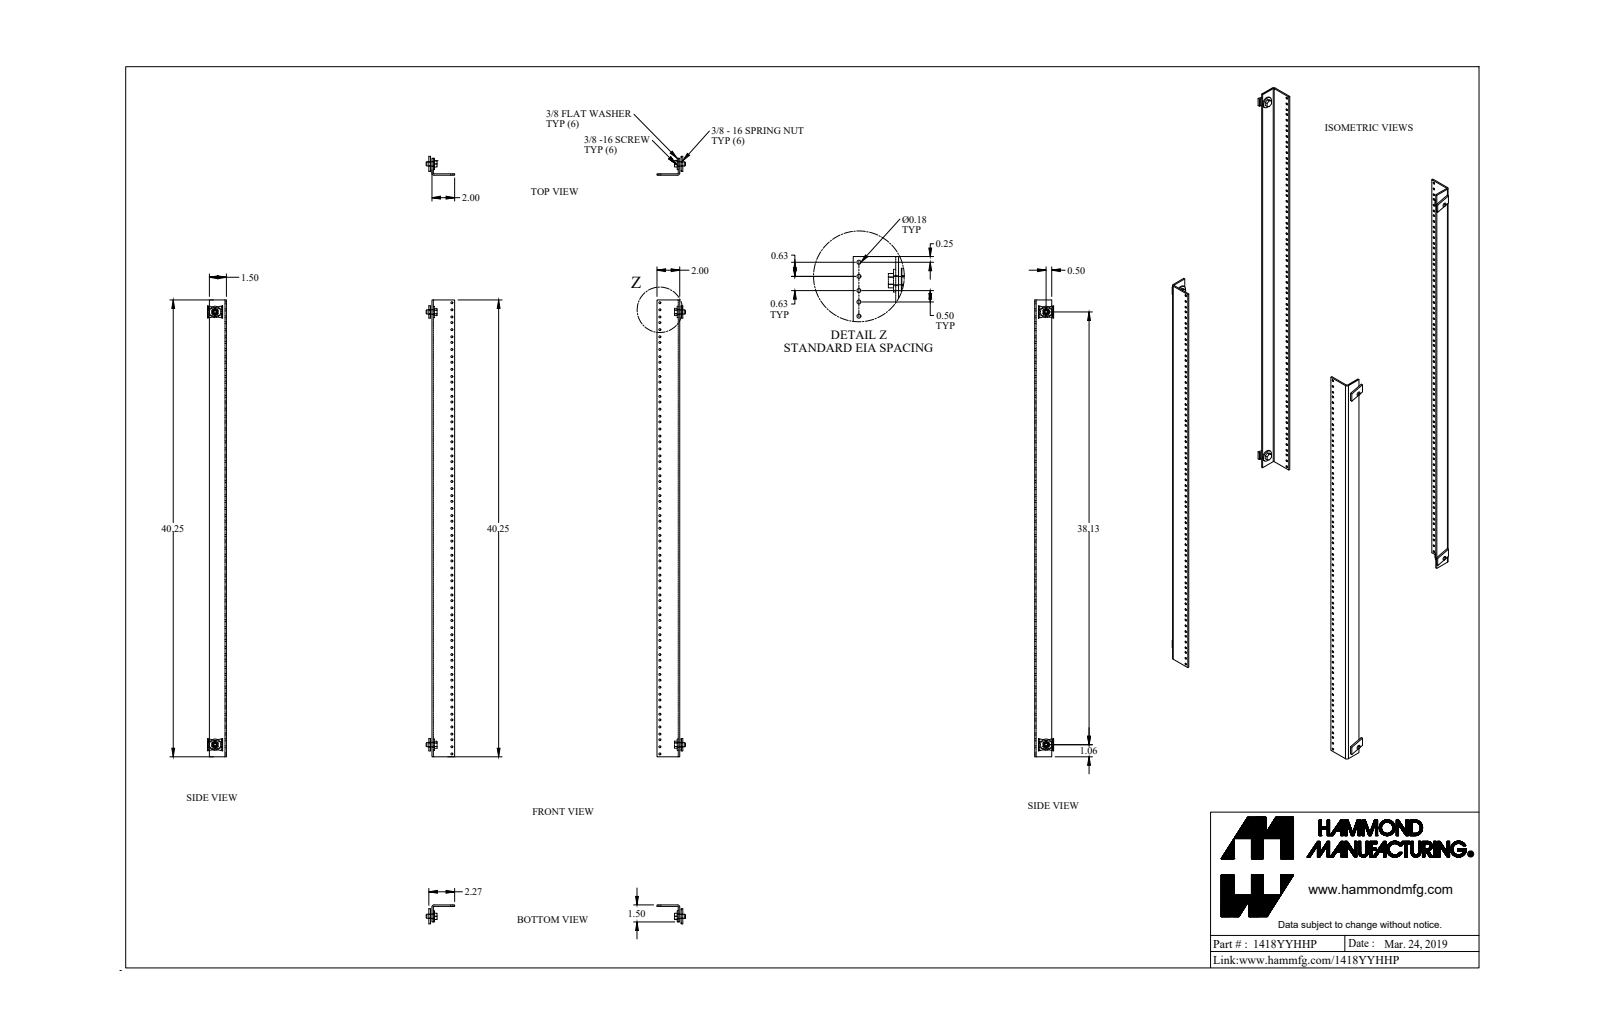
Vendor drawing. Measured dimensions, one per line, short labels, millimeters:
name: 1418YYHHP_Default
written by: SolidWorks 2019 (CONFIG_CONTROL_DESIGN)
unit: mm
bodies: 14 solids, 452 faces (124 planar, 320 cylindrical, 8 other)
size: 1022.4 × 580.5 × 42.4
volume: 561 400 mm³; area: 376 600 mm²
holes: 138× ⌀4.5, 2× ⌀8, 2× ⌀11.1, 2× ⌀11.3
bosses: 2× ⌀25.4, 2× ⌀9.1
rounds: 2× R1.5, 2× R4.7
face distances: 3.2, 3.2, 554.7, 548.4, 551.6, 551.6, 38.1, 34.9, 34.9, 50.8
hole spacings: 88.9, 44.5, 177.8, 133.4, 15.9, 28.6, 60.3, 73
